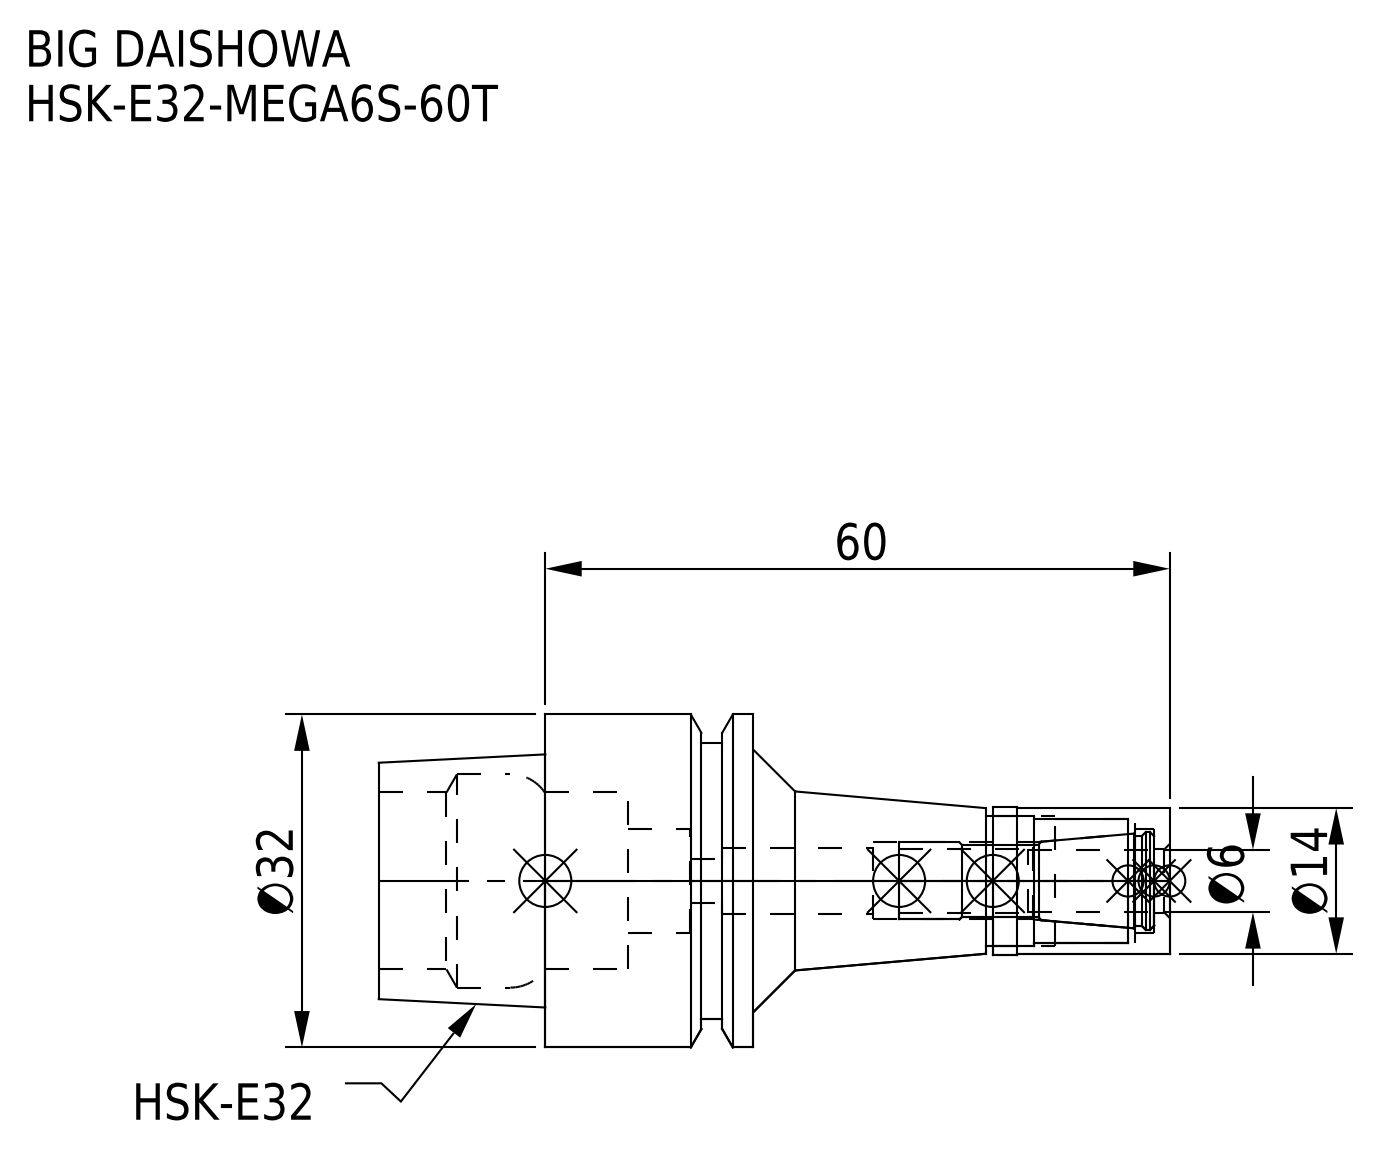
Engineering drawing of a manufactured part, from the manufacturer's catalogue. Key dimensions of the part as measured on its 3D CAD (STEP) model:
Part name (STEP PRODUCT): HSK-E32-MEGA6S-60T-060-FreeParts; MGN6S_1.stp; DXF_TEMP_ASSY_ASM_4_ASM.stp; HSK-E32-MEGA6S-60T_1.stp (+3 more)
STEP written by: SolidWorks 2019 (CONFIG_CONTROL_DESIGN)
Units: millimetres
Bodies: 2 solids, 74 faces (18 planar, 38 cylindrical, 18 other)
Overall size (bounding box): 76 × 32 × 32
Volume: 21 355 mm³ · Surface area: 10 661 mm²
Round holes (diameter × count): ⌀4.2 ×1, ⌀6.1 ×1, ⌀6.4 ×1, ⌀7.4 ×1, ⌀10 ×1, ⌀12 ×1, ⌀12.5 ×1, ⌀17 ×1, ⌀20.5 ×1
Round bosses / shafts (diameter × count): ⌀32 ×1, ⌀26.5 ×1, ⌀14.3 ×1, ⌀14 ×1
Main face-to-face distances: 20, 36, 16, 12.05, 7.95, 23.95, 17, 43, 40, 52.05
